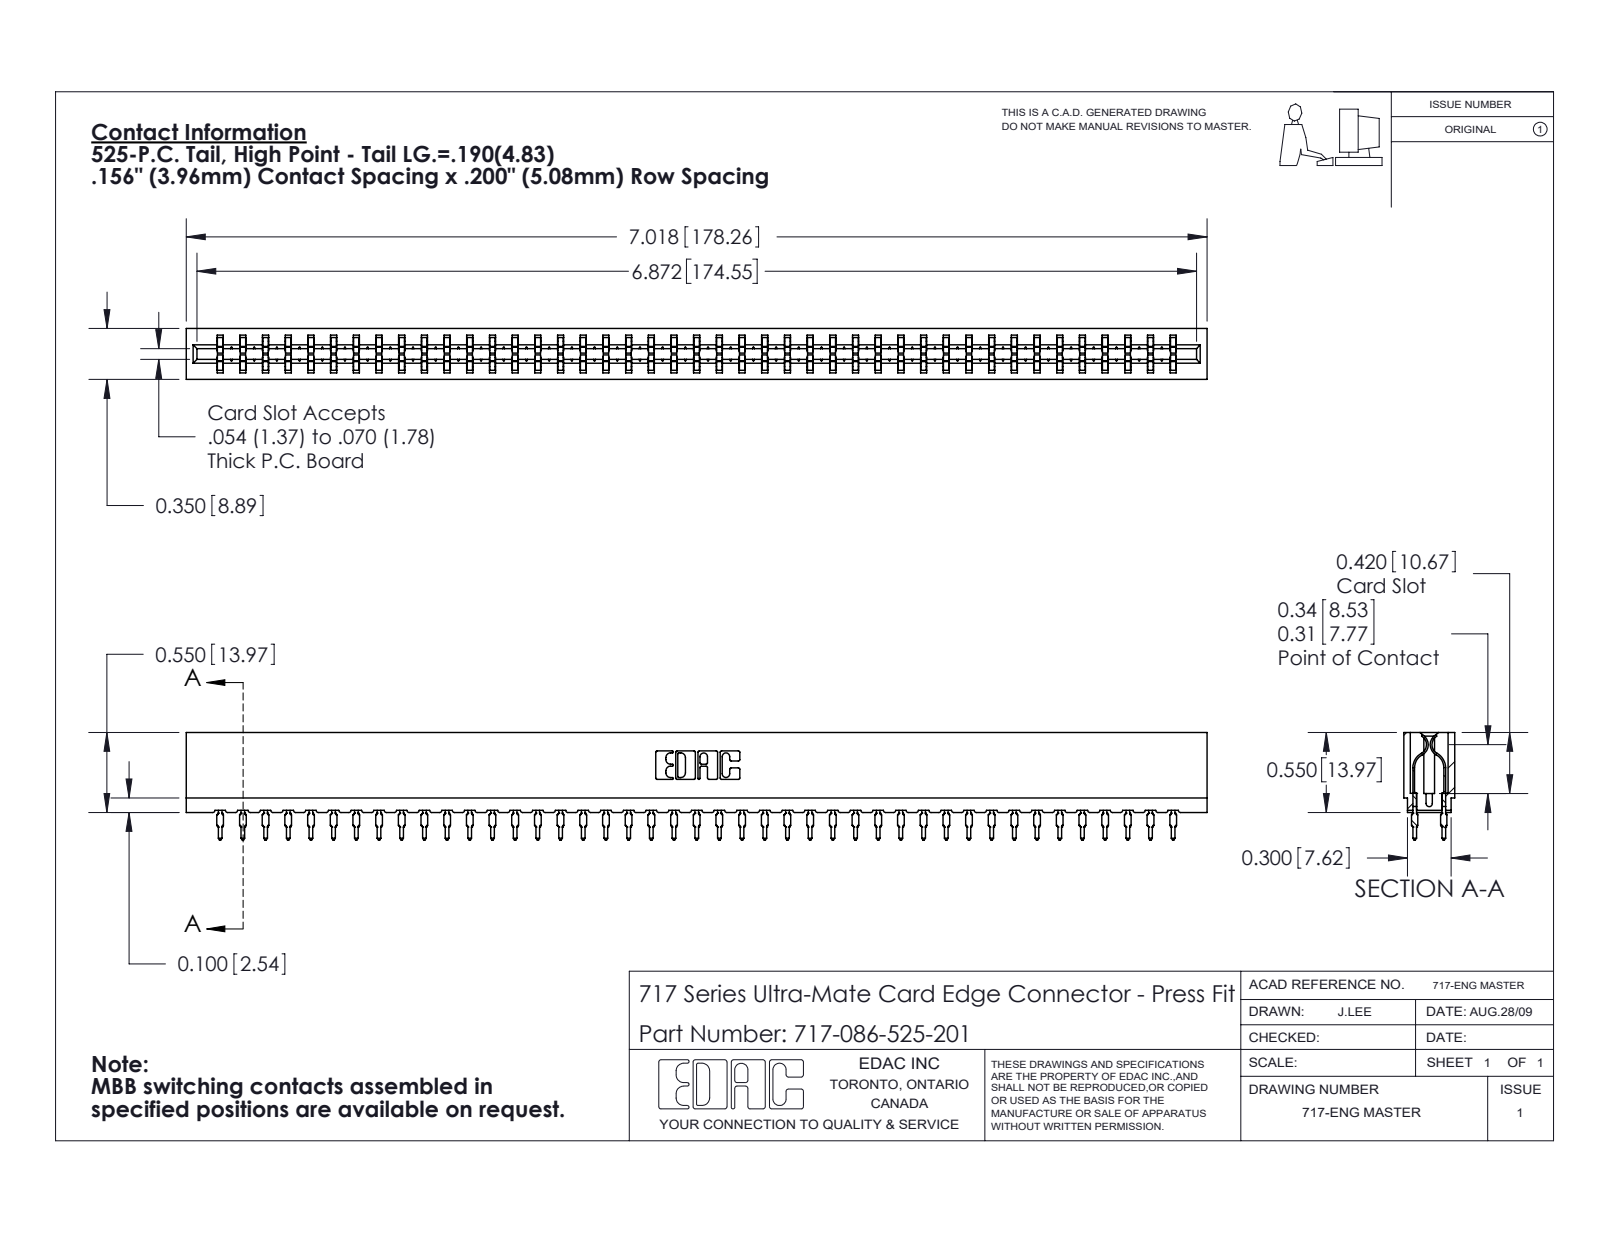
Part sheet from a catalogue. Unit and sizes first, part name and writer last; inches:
Units: inches
Overall size (bounding box): 7.018 × 0.739 × 0.35
Partial cylindrical surfaces — rounded edges, fillets, slot ends (radius × count): R0.021 ×172, R0.015 ×86, R0.01 ×22, R0.005 ×8, R0.011 ×8, R0.007 ×6, R0.031 ×6, R0.026 ×3
Main face-to-face distances: 0.212, 0.138, 0.35, 0.063, 0.287, 0.076, 0.149, 0.074, 0.045, 0.305
Volume: 0.941 in³ · Surface area: 36.43 in²
Bodies: 87 solids, 7834 faces (4053 planar, 1545 cylindrical, 2236 other)
Part name (STEP PRODUCT): 717-086-525-201; 745-292-001_525; 717 Part_Insulator Option - 06
STEP written by: SolidWorks 2020 (CONFIG_CONTROL_DESIGN)
